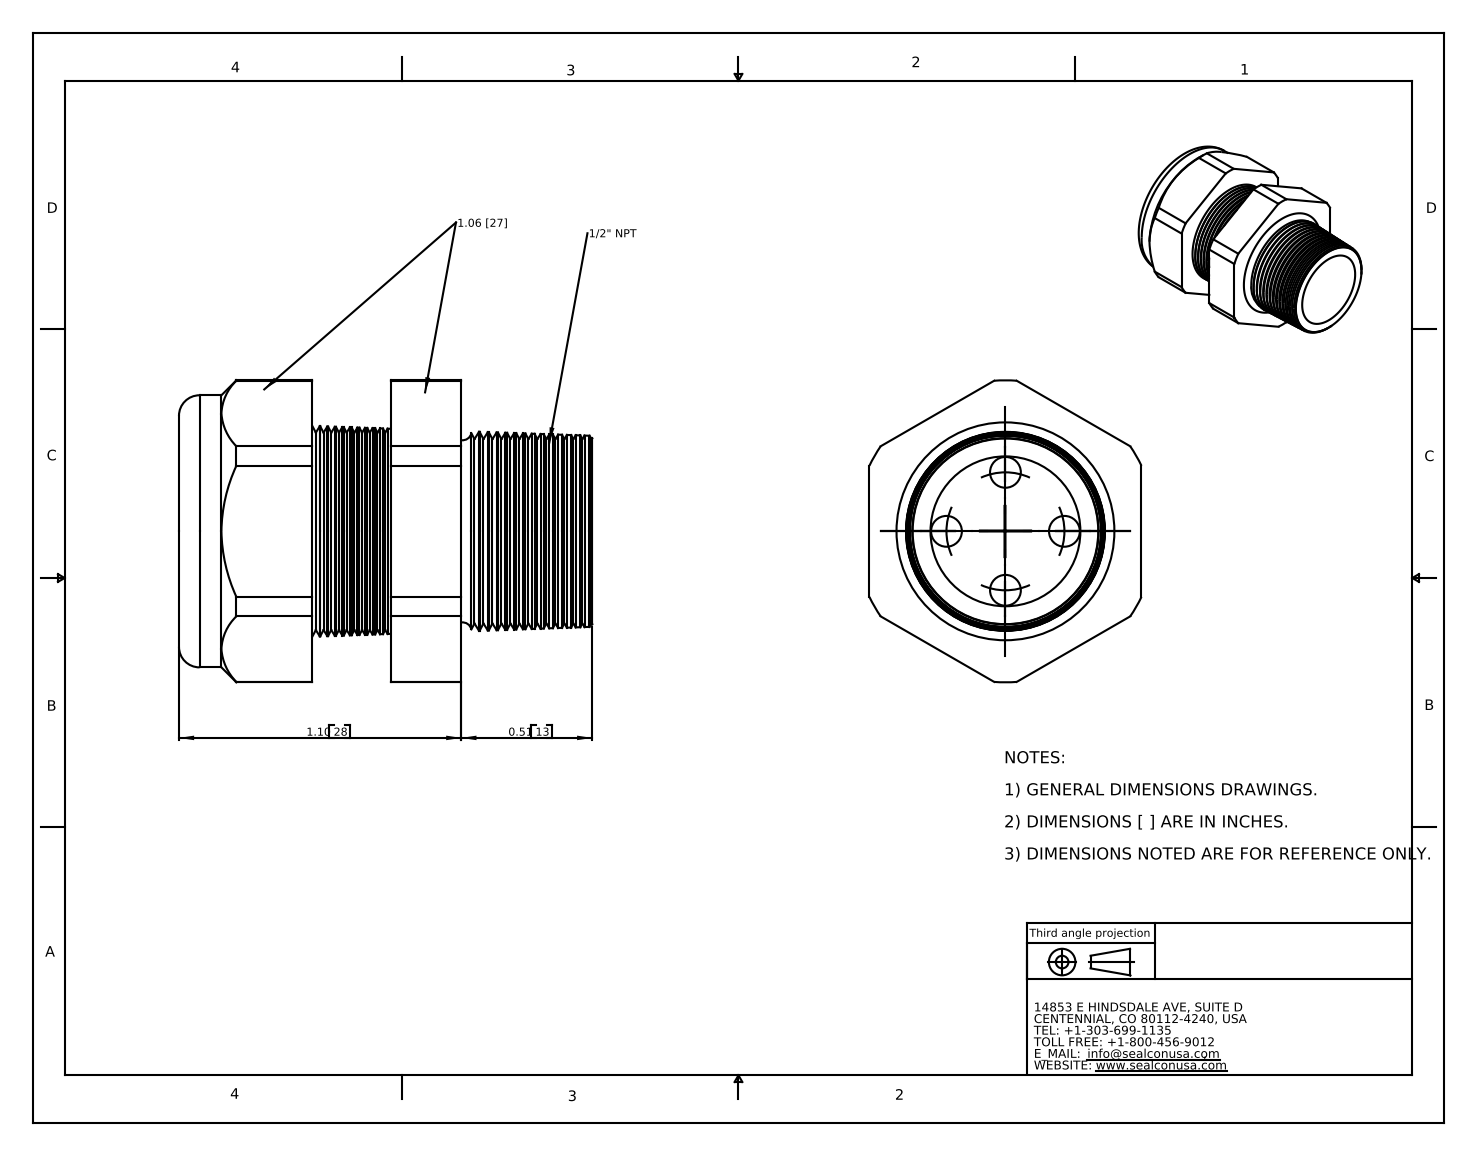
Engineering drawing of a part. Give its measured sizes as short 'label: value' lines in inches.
name: CD16N9-BK
written by: SolidWorks 2007 (CONFIG_CONTROL_DESIGN)
unit: in
bodies: 2 solids, 206 faces (20 planar, 28 cylindrical, 158 other)
size: 1.61 × 1.177 × 1.06
volume: 0.749 in³; area: 13.02 in²
holes: 4× ⌀0.12, 1× ⌀0.58, 1× ⌀0.6
bosses: 1× ⌀1.06
rounds: 1× R0.588
face distances: 1.06, 0.305, 0.58, 0.276, 0.52, 0.824, 1.1, 0.35, 0.17, 0.474
hole spacings: 0.23, 0.325, 0.46
